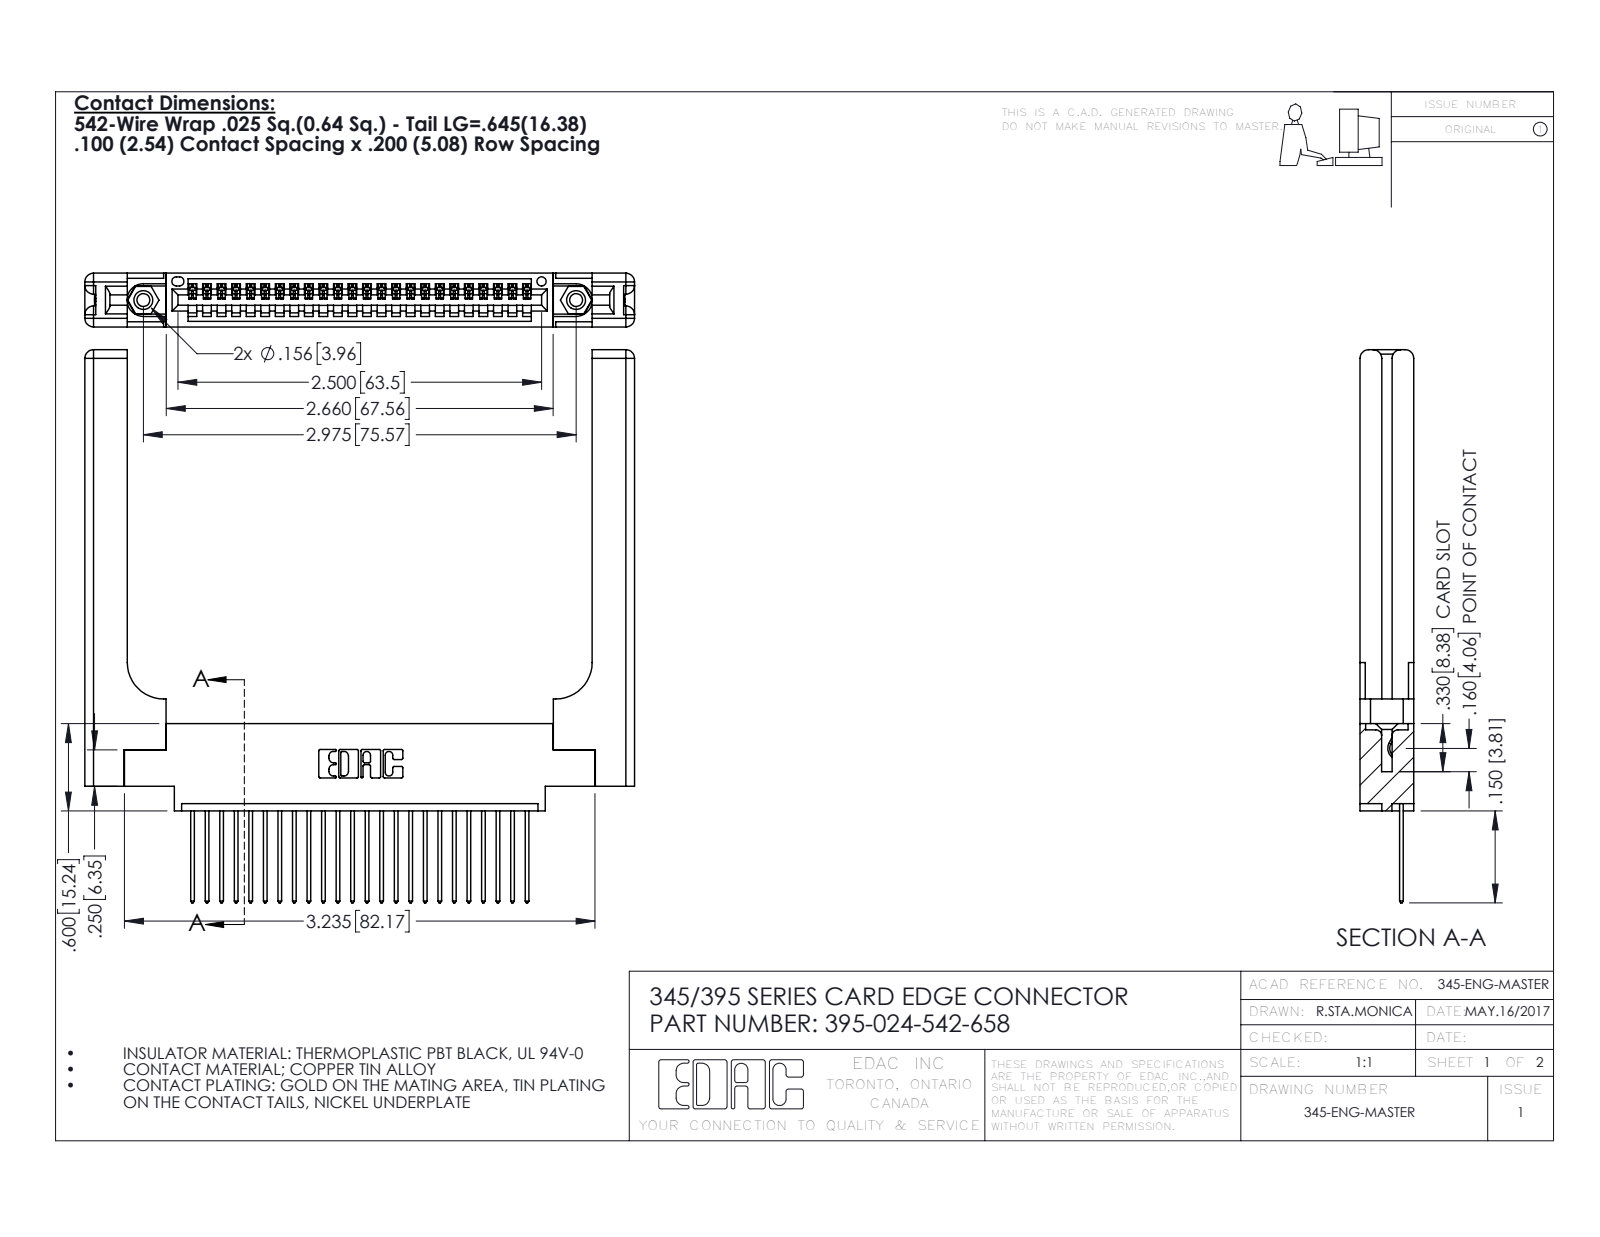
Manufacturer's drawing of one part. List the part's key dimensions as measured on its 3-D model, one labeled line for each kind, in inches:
Part name (STEP PRODUCT): 345-250-001_345-250-001-102; 345-292-001_345-293-142; 395-024-542-658; 345-220-058_345-220-058 (+1 more)
STEP written by: SolidWorks 2016 (CONFIG_CONTROL_DESIGN)
Units: inches
Bodies: 29 solids, 1778 faces (1192 planar, 526 cylindrical, 60 other)
Overall size (bounding box): 3.802 × 3.779 × 0.37
Volume: 1.063 in³ · Surface area: 26.92 in²
Round holes (diameter × count): ⌀0.089 ×2, ⌀0.125 ×2, ⌀0.156 ×2, ⌀0.064 ×1
Round bosses / shafts (diameter × count): ⌀0.155 ×2
Partial cylindrical surfaces — rounded edges, fillets, slot ends (radius × count): R0.006 ×48, R0.01 ×48, R0.01 ×22, R0.06 ×16, R0.007 ×6, R0.031 ×6, R0.026 ×3, R0.03 ×2
Main face-to-face distances: 0.37, 0.072, 0.298, 0.098, 0.272, 0.025, 0.148, 0.15, 0.077, 0.2
Hole centre spacings: 0.27, 2.741, 2.975
